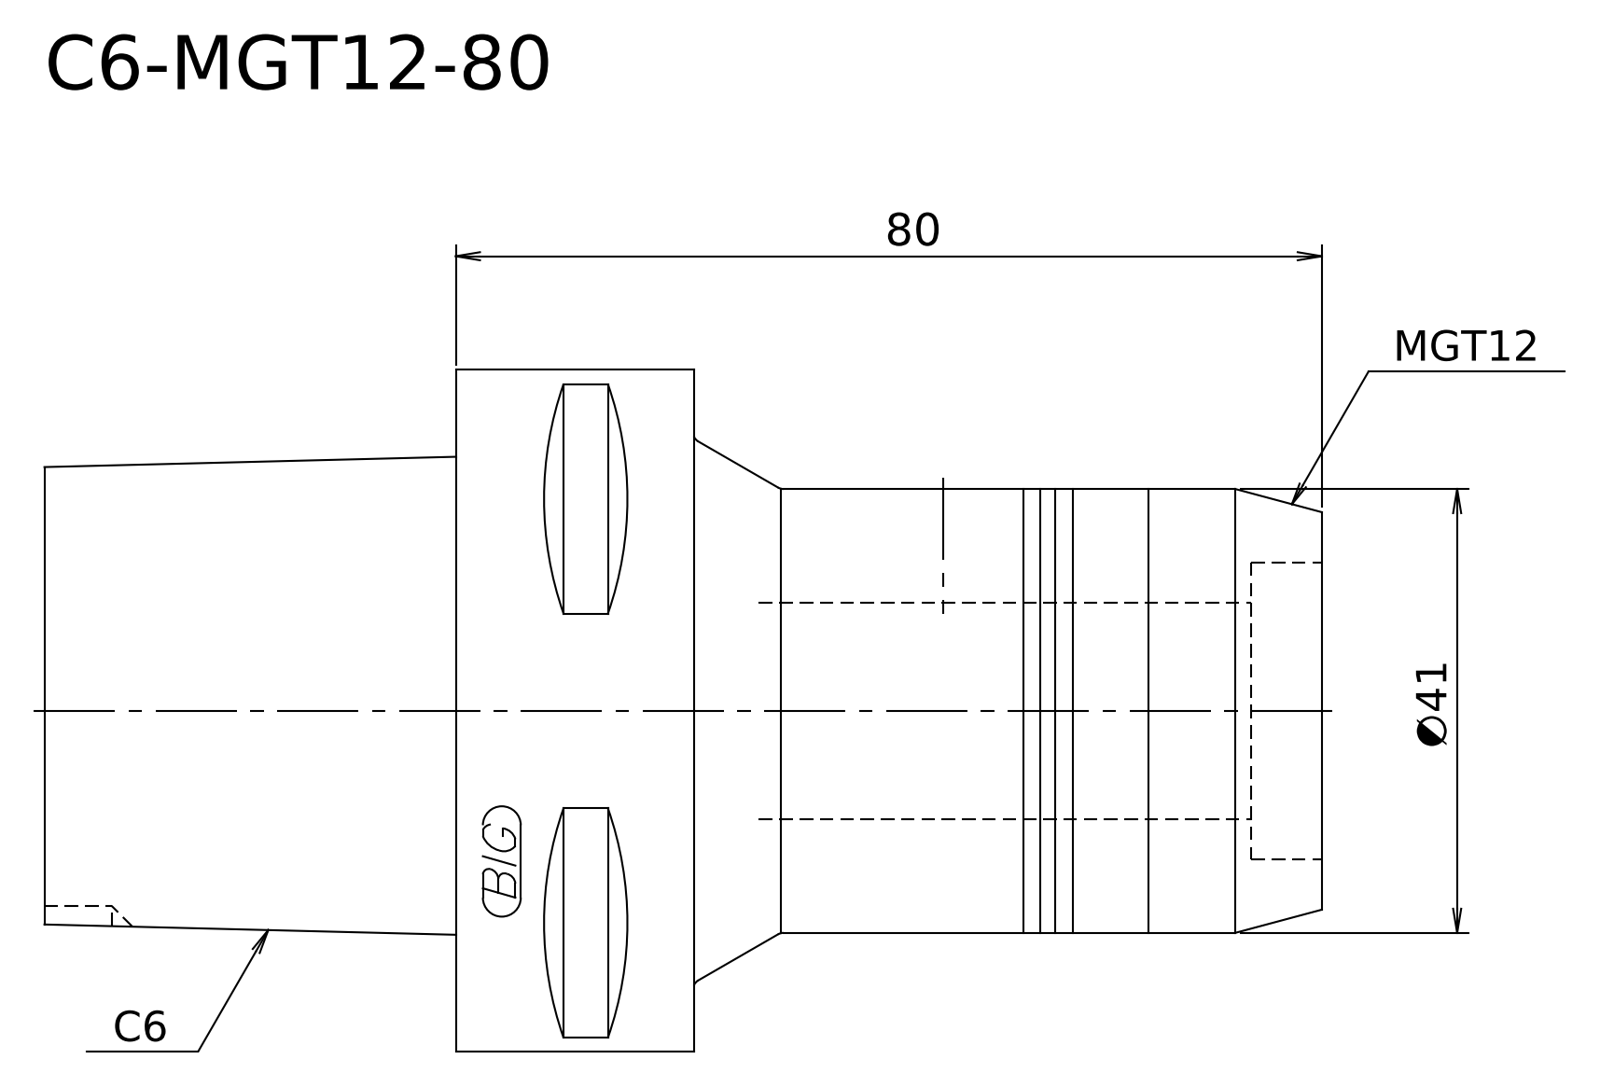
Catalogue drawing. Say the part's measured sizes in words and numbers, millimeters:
Its 3-D file was written by "Kubotek KeyCreator V8.5.1 (14335) (CONFIG_CONTROL_DESIGN)". It is 1 solid with 11 faces: 4 planar, 2 cylindrical and 5 other. Overall it measures 118 by 62.98 by 62.98 millimeters. Its volume is 201 395 cubic millimeters and its surface area 22 435 square millimeters. Round bosses or shafts: 1 of diameter 62.98, 1 of diameter 41. The main face-to-face distances are 38, 22, 60, 58, 80, 118.
